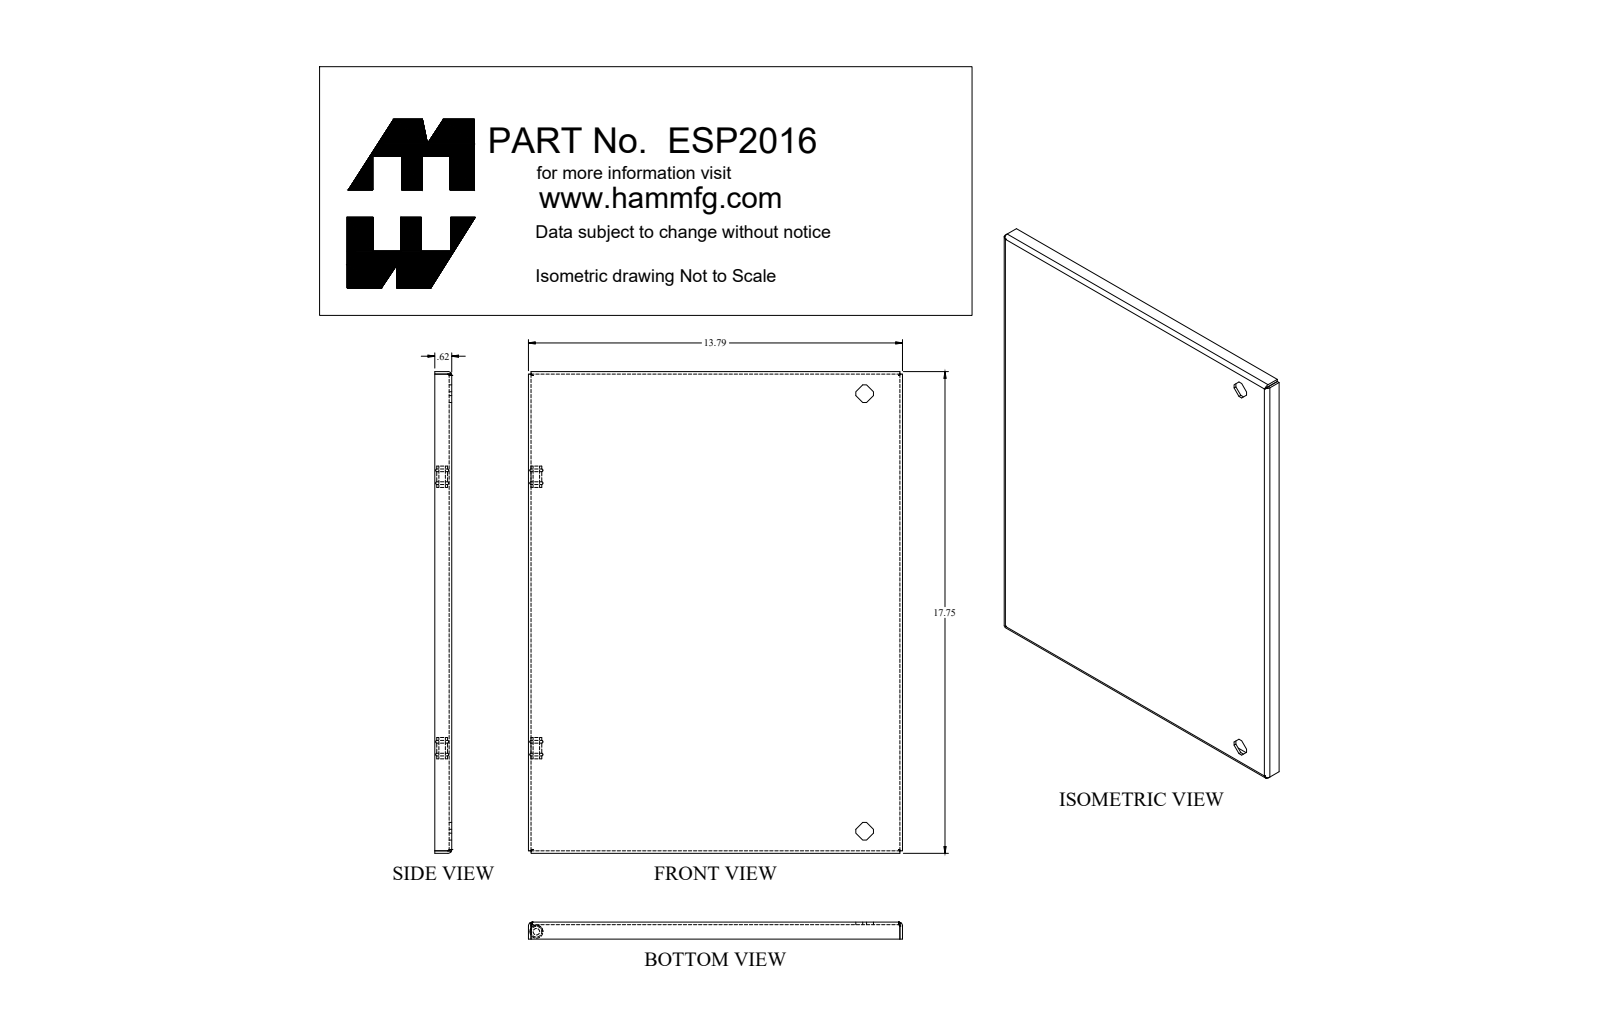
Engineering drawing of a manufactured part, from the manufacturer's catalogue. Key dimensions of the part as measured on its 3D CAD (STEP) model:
Part name (STEP PRODUCT): ESP2016
STEP written by: SolidWorks 2018 (AUTOMOTIVE_DESIGN)
Units: inches
Bodies: 13 solids, 584 faces (354 planar, 174 cylindrical, 56 other)
Overall size (bounding box): 17.75 × 15.706 × 9.953
Volume: 39.21 in³ · Surface area: 1 024 in²
Round holes (diameter × count): ⌀0.136 ×2, ⌀0.242 ×2, ⌀0.516 ×2
Round bosses / shafts (diameter × count): ⌀0.232 ×6, ⌀0.788 ×2, ⌀0.535 ×2, ⌀0.496 ×2, ⌀0.435 ×2, ⌀0.356 ×2
Partial cylindrical surfaces — rounded edges, fillets, slot ends (radius × count): R0.048 ×28, R0.01 ×24, R0.036 ×6, R0.108 ×6, R0.06 ×4, R0.143 ×4, R0.153 ×4, R0.156 ×4
Main face-to-face distances: 0.095, 0.072, 0.038, 14.008, 0.813, 0.775, 0.775, 16.062, 14.893, 14.08
Hole centre spacings: 10, 16.159
